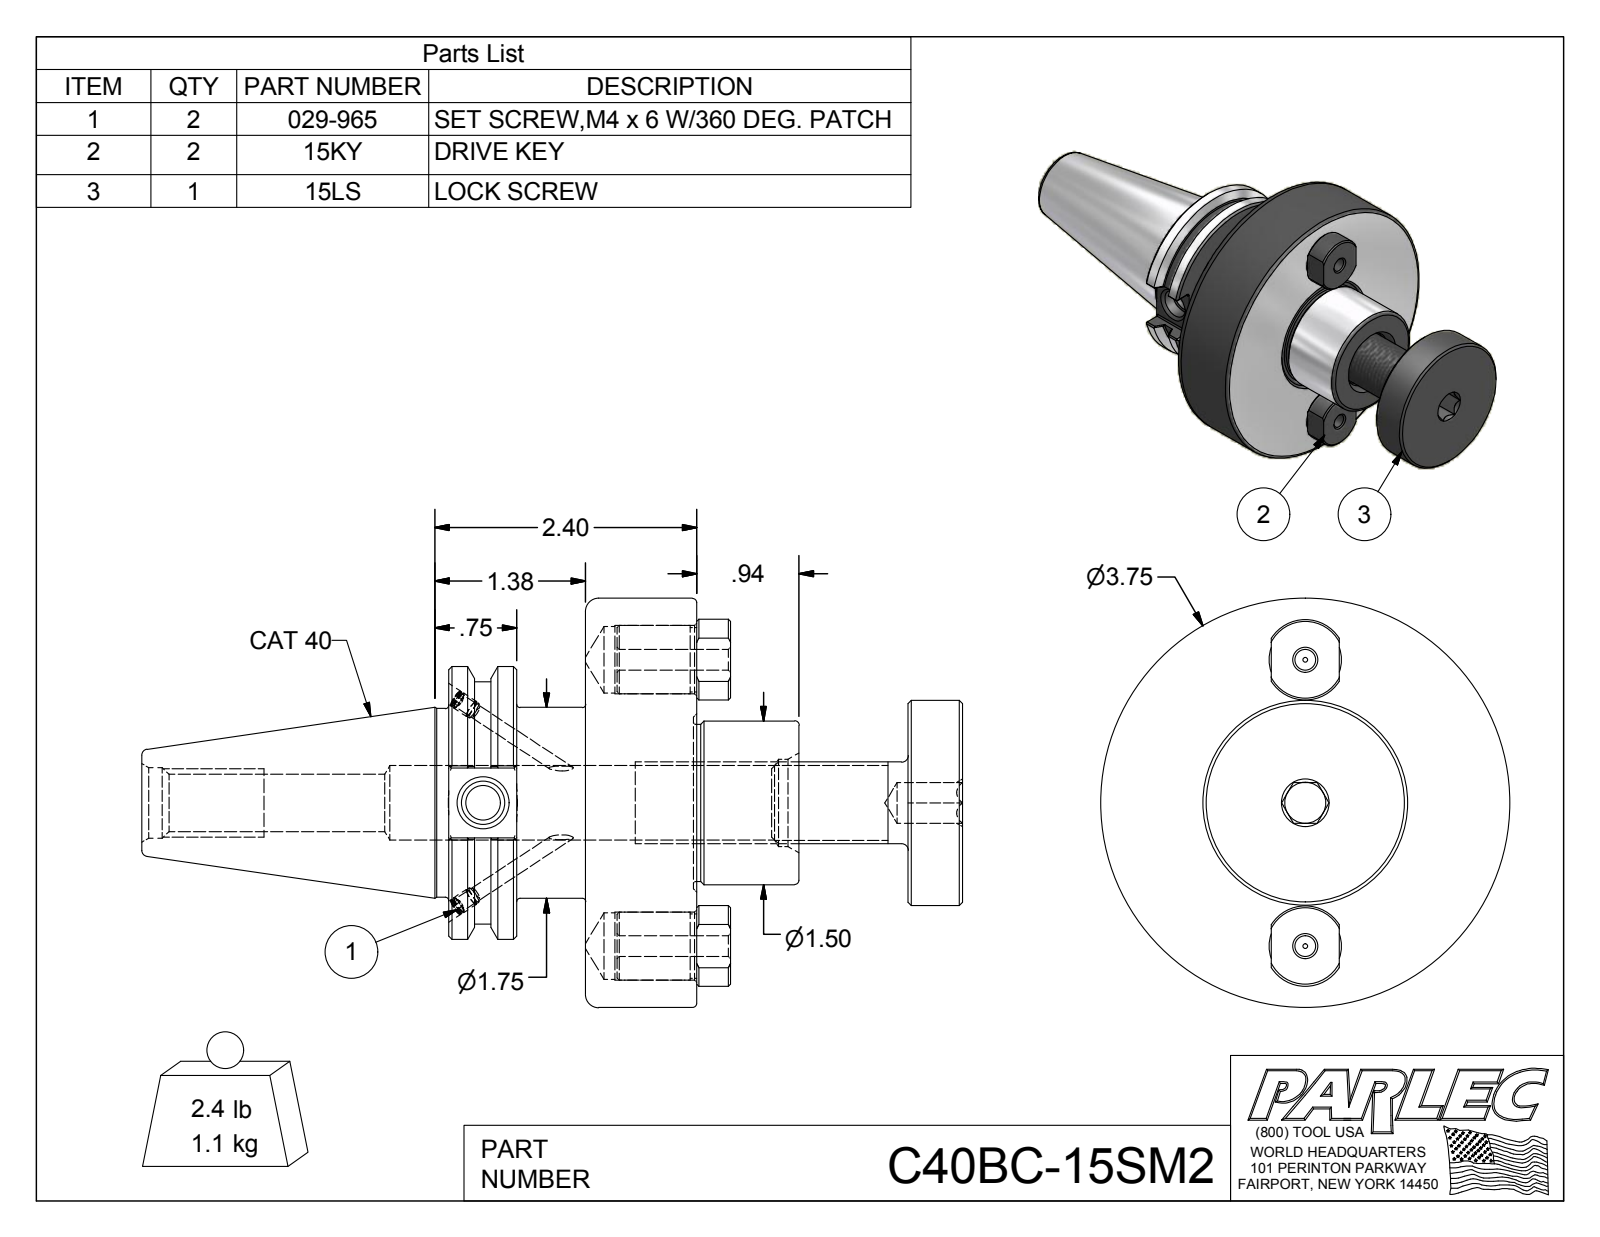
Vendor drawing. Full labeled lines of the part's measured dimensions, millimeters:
Part name (STEP PRODUCT): C40BC-15SM2; C40BC-15SM2-1; 15KY; 15LS (+1 more)
STEP written by: Autodesk Inventor 2012 (AUTOMOTIVE_DESIGN)
Units: millimetres
Bodies: 6 solids, 206 faces (85 planar, 56 cylindrical, 65 other)
Overall size (bounding box): 191.1 × 95.3 × 95.3
Volume: 348 200 mm³ · Surface area: 62 740 mm²
Round holes (diameter × count): ⌀3.3 ×2, ⌀4.1 ×2, ⌀4.8 ×2, ⌀15.5 ×2, ⌀15.8 ×2, ⌀8 ×1, ⌀9.5 ×1, ⌀10.1 ×1, ⌀13.4 ×1, ⌀16.5 ×1, ⌀17.3 ×1, ⌀20.3 ×1
Round bosses / shafts (diameter × count): ⌀15.9 ×2, ⌀15 ×2, ⌀4.2 ×2, ⌀4 ×2, ⌀95.3 ×1, ⌀63.5 ×1, ⌀56.4 ×1, ⌀47.8 ×1
Partial cylindrical surfaces — rounded edges, fillets, slot ends (radius × count): R0.5 ×12, R9.4 ×2
Main face-to-face distances: 25.9, 87.8, 61.9, 75.1, 49.2, 12.7, 31.9, 57.8, 107, 119.7
Hole centre spacings: 33.3, 66.6
